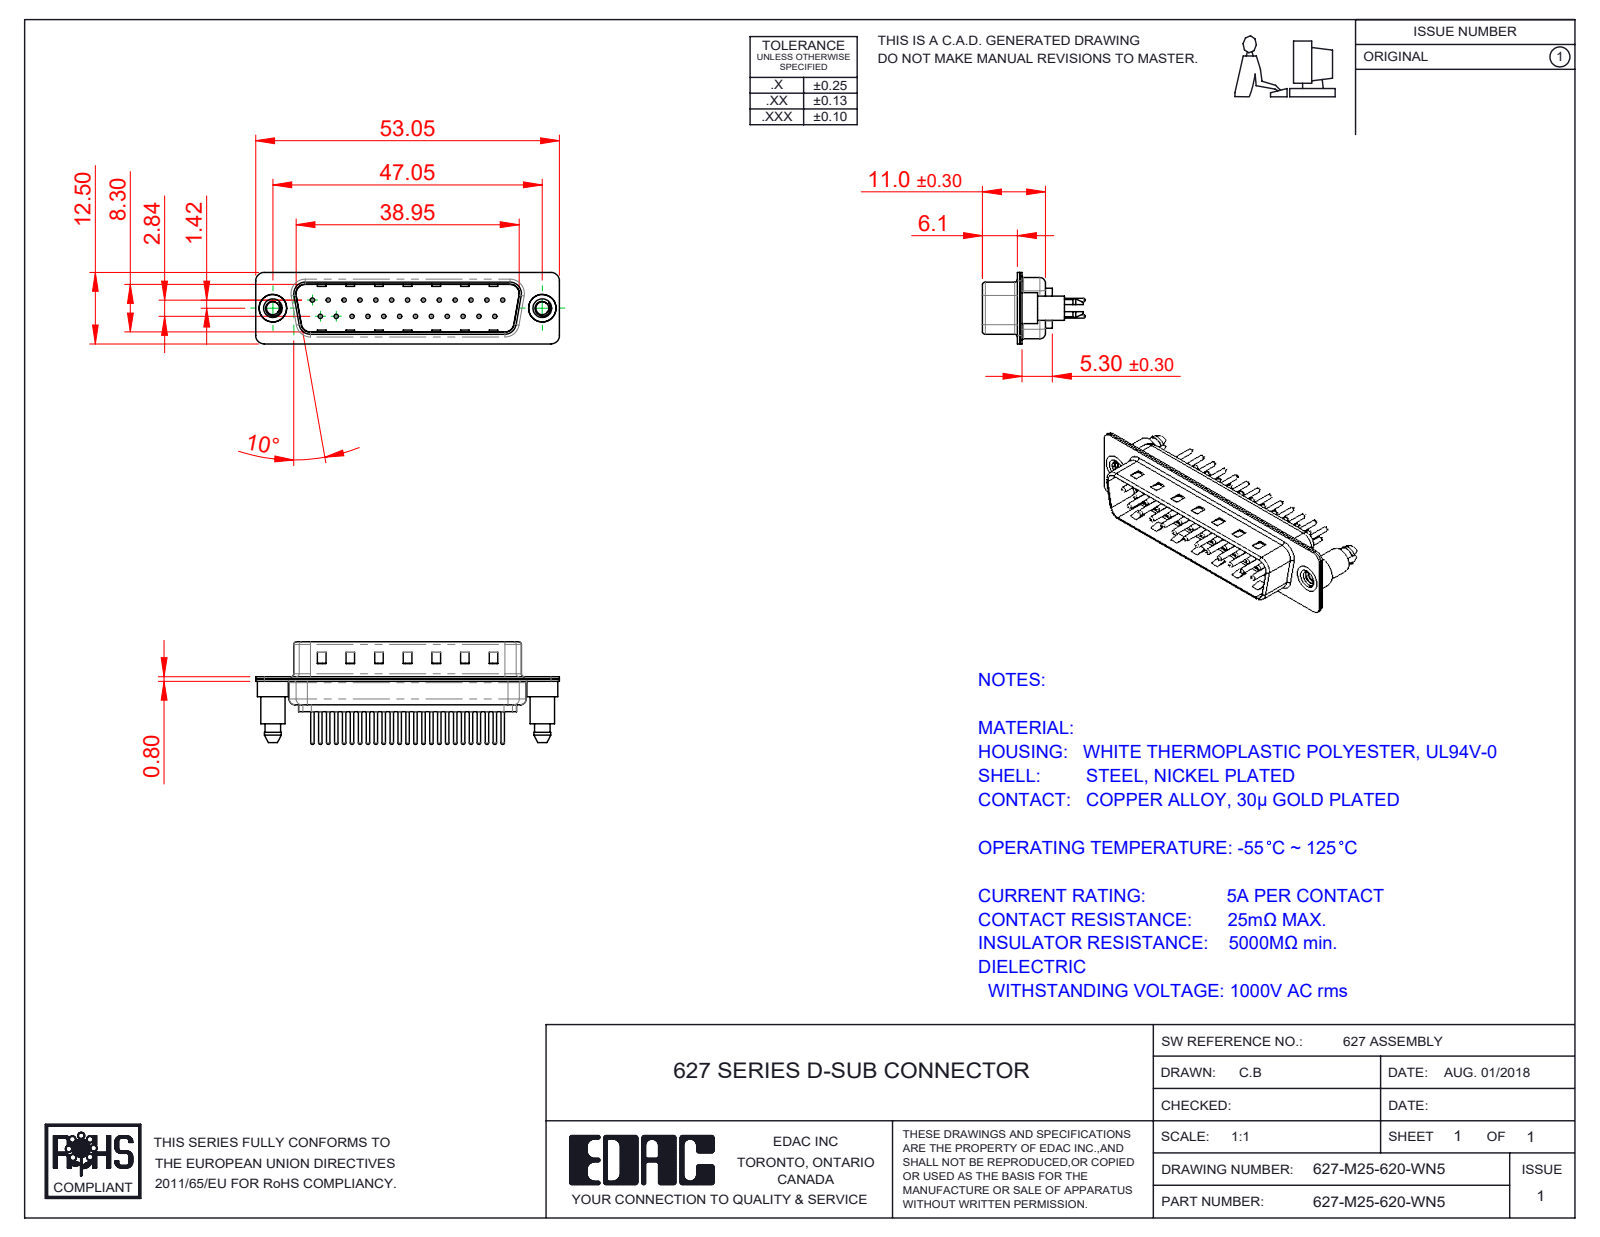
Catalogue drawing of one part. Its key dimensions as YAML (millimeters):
part_name: "627M Contact Row 2_20; 627M Contact Row 1_20; 627M Shell Front_25 Contacts; 627M Housing_25 Contacts (+3 more)"
step_written_by: "SolidWorks 2020 (CONFIG_CONTROL_DESIGN)"
units: millimeters
bodies: {solids: 30, faces: 1351, planar: 362, cylindrical: 519, other: 470}
overall_size: [53.05, 17.9, 12.5]
volume: 2853
surface_area: 7176
round_holes:
  - {diameter: 0.75, count: 25}
  - {diameter: 1.6, count: 25}
  - {diameter: 2, count: 25}
  - {diameter: 2.26, count: 2}
  - {diameter: 4, count: 2}
  - {diameter: 4.8, count: 2}
round_bosses_or_shafts:
  - {diameter: 1.5, count: 25}
  - {diameter: 0.6, count: 25}
  - {diameter: 5.4, count: 2}
  - {diameter: 4.9, count: 2}
  - {diameter: 4.25, count: 2}
partial_cylinders:
  - {radius: 1.5, count: 18}
  - {radius: 2, count: 12}
  - {radius: 1.6, count: 10}
  - {radius: 0.5, count: 8}
  - {radius: 0.25, count: 4}
  - {radius: 0.6, count: 4}
  - {radius: 0.65, count: 4}
  - {radius: 0.9, count: 4}
face_to_face_distances: [0.4, 0.8, 9.5, 9.1, 8.7, 9.9, 1.2, 6.1, 5.7, 0.75]
hole_center_spacings: [3.16, 2.77, 5.54, 8.31, 11.08, 13.85, 16.62, 5.03]
